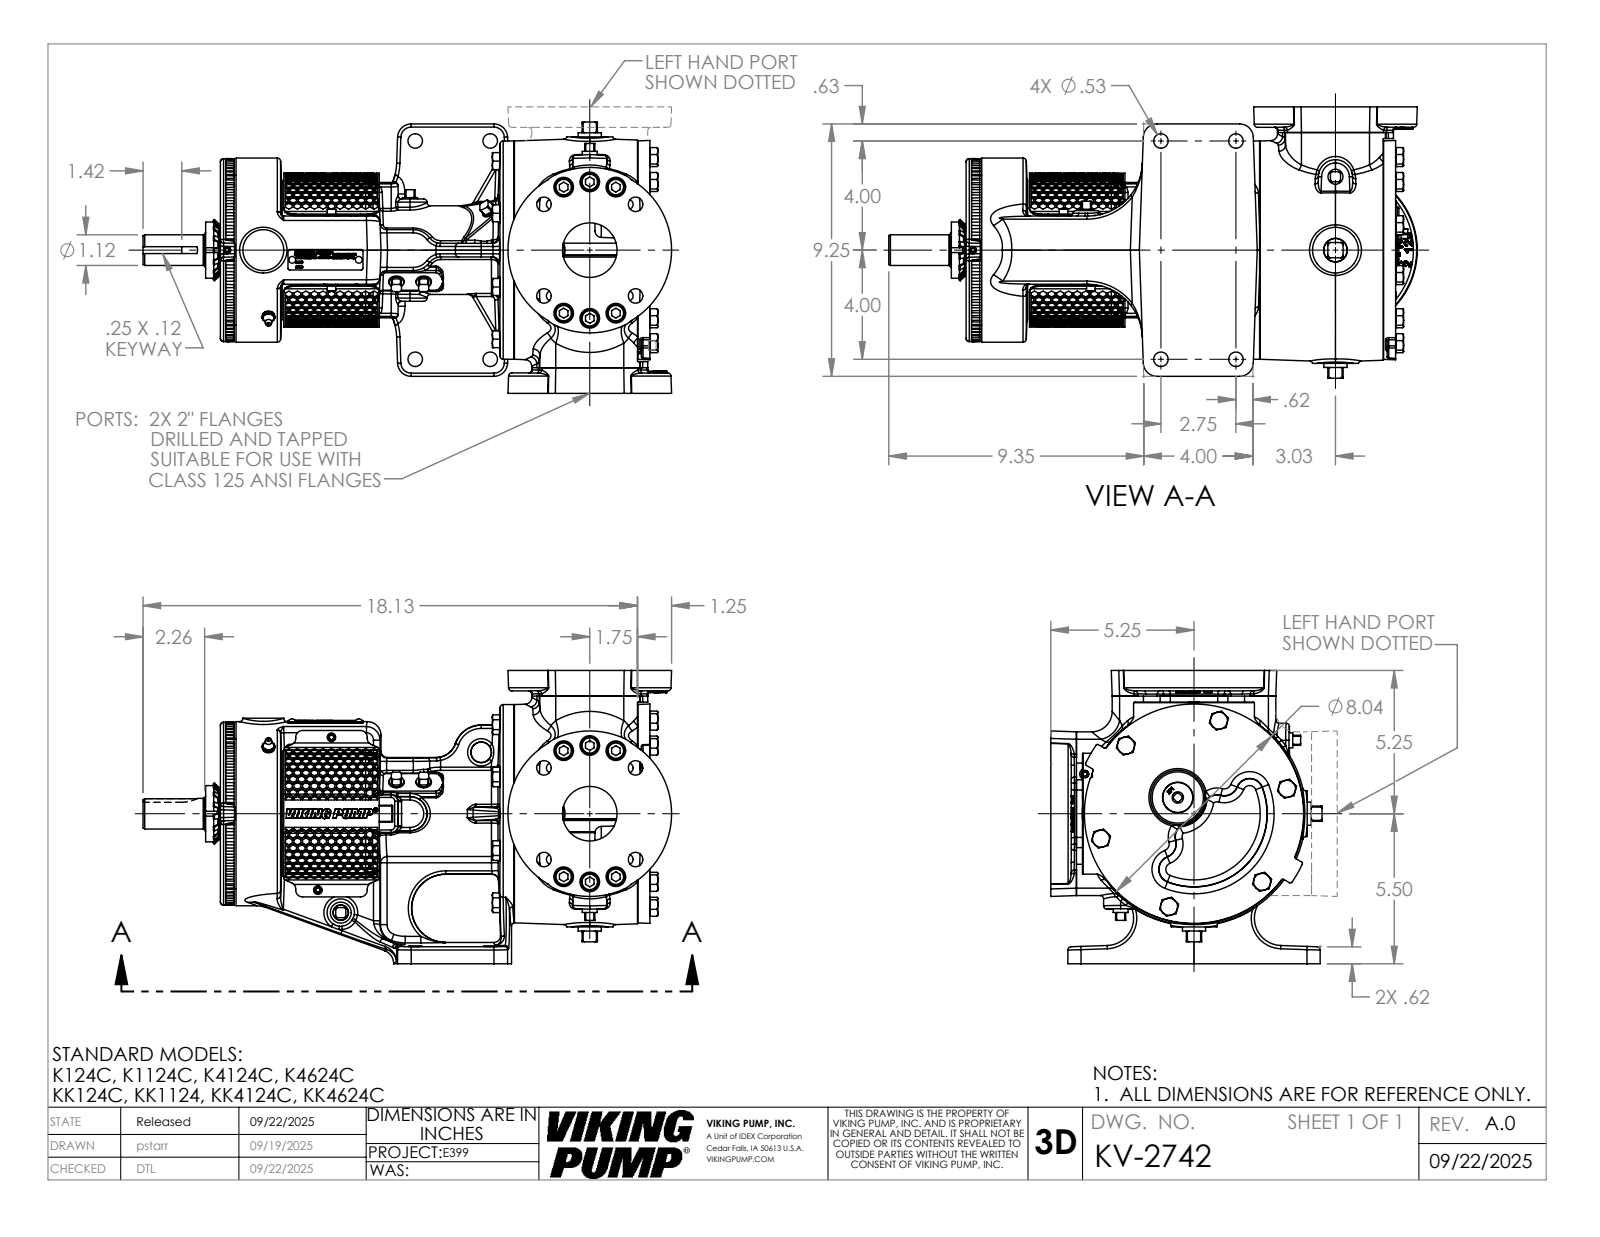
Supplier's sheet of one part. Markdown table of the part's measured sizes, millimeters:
| quantity | value |
| --- | --- |
| part name | KV-2742 |
| STEP written by | SolidWorks 2024 (AUTOMOTIVE_DESIGN) |
| units | millimeters |
| bodies | 1 solid, 4836 faces (1526 planar, 687 cylindrical, 2623 other) |
| overall size | 492.23 × 273.05 × 252.6 |
| volume | 8 616 000 mm³ |
| surface area | 645 825 mm² |
| round holes (diameter × count) | 13.49 × 12, 18.26 × 12, 6.35 × 9, 9.35 × 8, 19.81 × 8, 5.02 × 6, 4.04 × 2, 7.94 × 2, 50.8 × 2, 6.53 × 1, 11.51 × 1, 28.5 × 1 |
| round bosses / shafts (diameter × count) | 15.88 × 23, 15.87 × 3, 7.92 × 3, 4.83 × 3, 203.2 × 1, 171.45 × 1, 139.62 × 1, 133.27 × 1 |
| partial cylindrical surfaces (radius × count) | 0.25 × 96, 3.05 × 77, 0.76 × 18, 6.1 × 18, 25.4 × 18, 3.05 × 16, 6.35 × 10, 12.7 × 10 |
| main face-to-face distances | 273.05, 400.03, 12.7, 135.23, 264.8, 120.65, 19.05, 14.58, 385.45, 25.4 |
| hole center spacings | 76.2, 26.16, 63.5, 6.94, 24.78, 34.96, 55.56, 60.59 |
